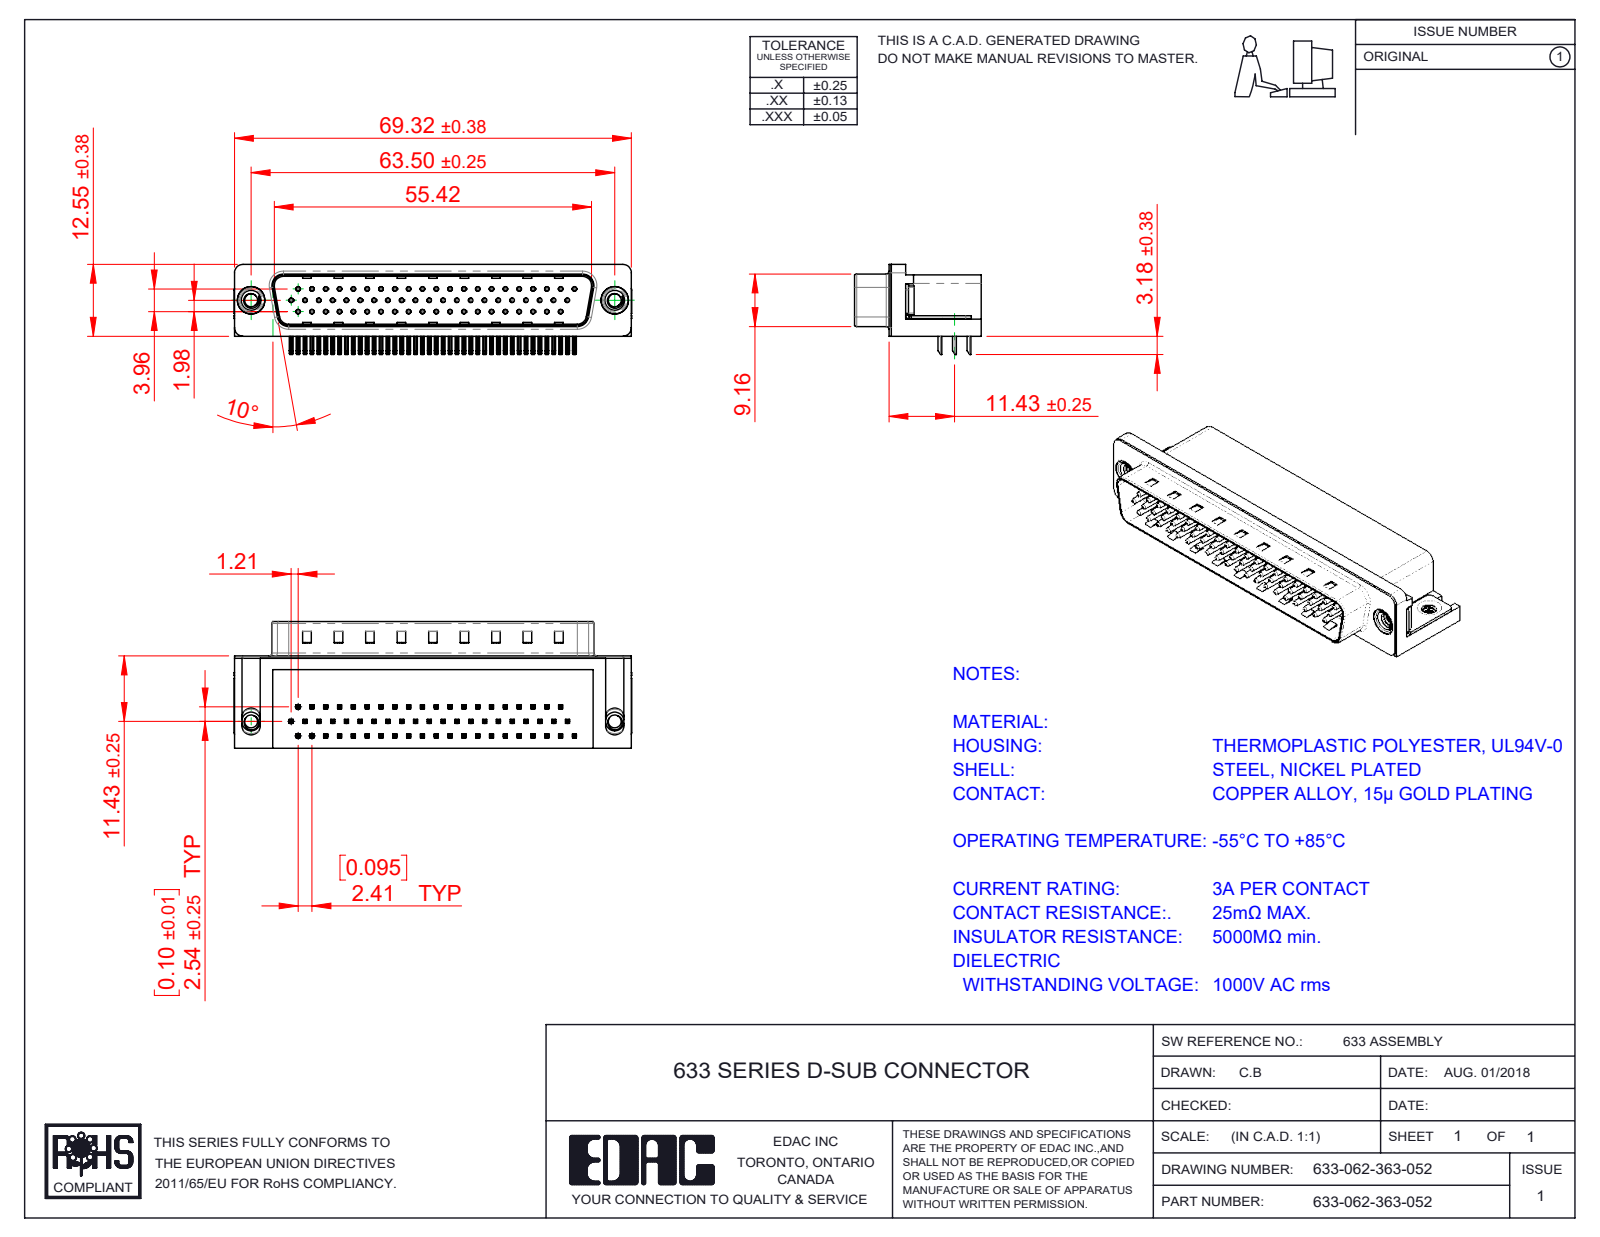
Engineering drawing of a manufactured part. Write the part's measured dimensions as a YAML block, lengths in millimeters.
part_name: "633-062-363-052; 633 Shell_62 Contact; 633 Contact Bottom; 633 Housing_62 Contact (+4 more)"
step_written_by: "SolidWorks 2016 (CONFIG_CONTROL_DESIGN)"
units: millimeters
bodies: {solids: 68, faces: 5106, planar: 3213, cylindrical: 1454, other: 439}
overall_size: [69.4, 22.1, 15.73]
volume: 11068
surface_area: 13485
round_holes:
  - {diameter: 0.35, count: 62}
  - {diameter: 0.8, count: 62}
  - {diameter: 2.26, count: 4}
  - {diameter: 4, count: 2}
  - {diameter: 4.8, count: 2}
  - {diameter: 5, count: 2}
round_bosses_or_shafts:
  - {diameter: 0.75, count: 62}
  - {diameter: 4.9, count: 2}
  - {diameter: 4.75, count: 2}
  - {diameter: 3.9, count: 2}
  - {diameter: 3.26, count: 2}
partial_cylinders:
  - {radius: 0.25, count: 256}
  - {radius: 0.12, count: 124}
  - {radius: 1, count: 16}
  - {radius: 0.5, count: 9}
  - {radius: 1.6, count: 8}
  - {radius: 1.5, count: 7}
  - {radius: 0.9, count: 4}
  - {radius: 2, count: 4}
face_to_face_distances: [0.4, 10.35, 15.7, 8.76, 2.9, 2.5, 2.54, 8.36, 2.1, 16.1]
hole_center_spacings: [2.41, 4.82, 7.24, 9.65, 14.48, 16.89, 4.83, 7.23]
